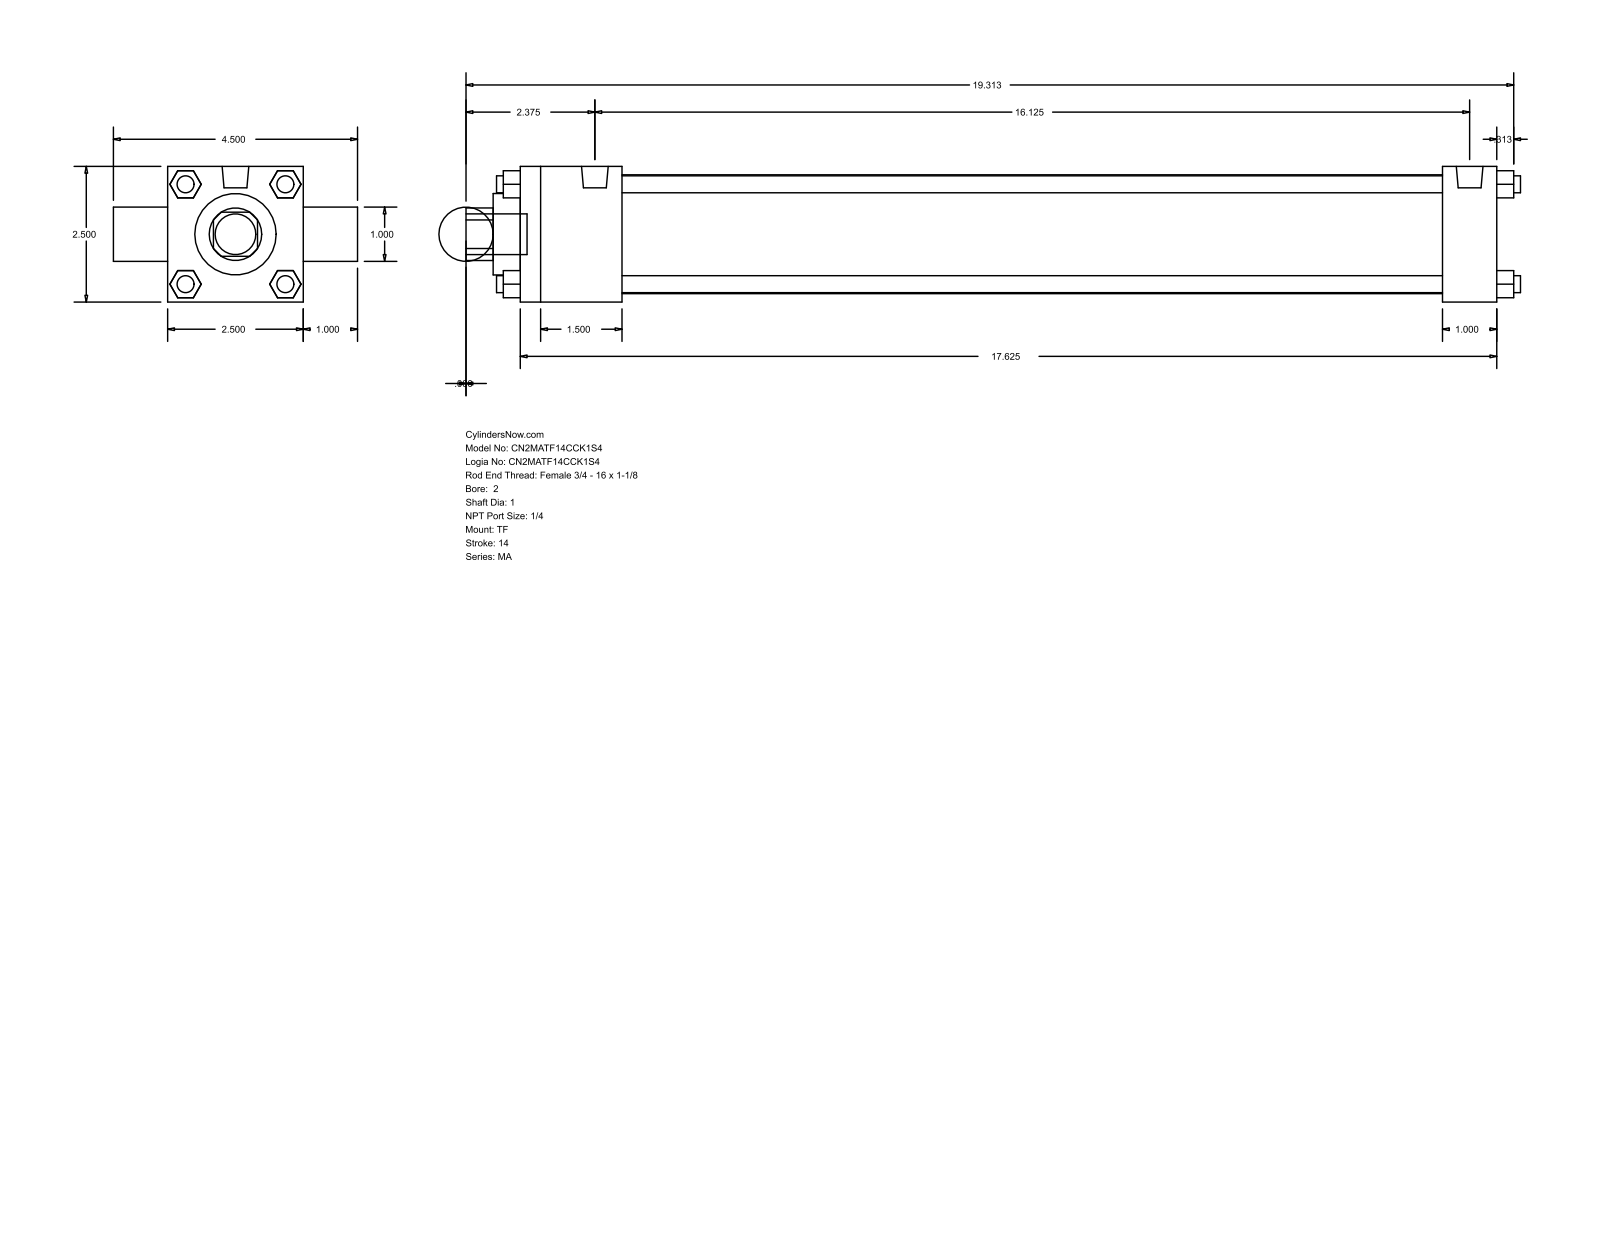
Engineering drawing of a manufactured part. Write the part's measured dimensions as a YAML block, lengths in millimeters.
part_name: "MA_TF__0200_1"
step_written_by: "GSSL Pune (CONFIG_CONTROL_DESIGN)"
units: millimeters
bodies: {solids: 0, faces: 120, planar: 92, cylindrical: 28, other: 0}
overall_size: [493.71, 114.3, 63.5]
round_holes:
  - {diameter: 25.4, count: 2}
  - {diameter: 38.1, count: 1}
  - {diameter: 55.63, count: 1}
round_bosses_or_shafts:
  - {diameter: 7.94, count: 7}
  - {diameter: 12.49, count: 2}
  - {diameter: 19.05, count: 1}
partial_cylinders:
  - {radius: 12.29, count: 1}
face_to_face_distances: [63.5, 25.4, 457.2, 12.7, 47.63, 431.8, 384.17, 409.57, 88.9, 40.47]
